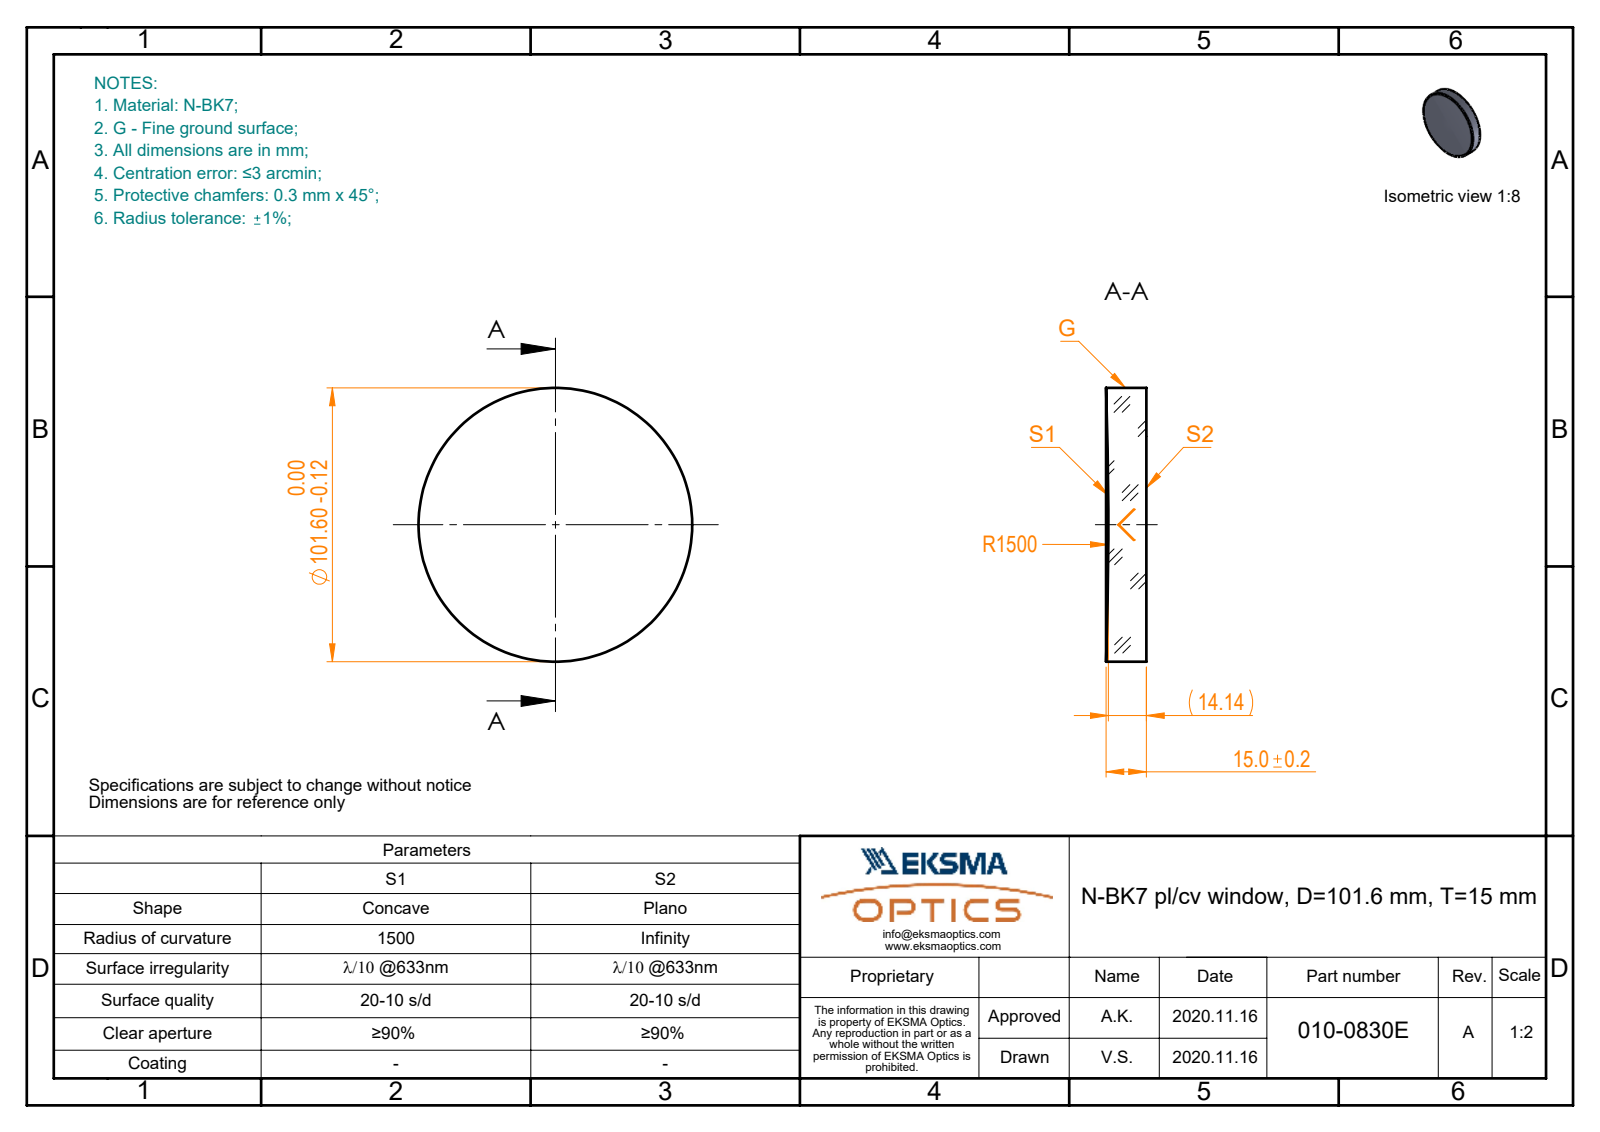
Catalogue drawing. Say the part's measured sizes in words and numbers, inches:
The part is named "010-0830E_N-BK7_PCV_window". Its 3-D file was written by "SolidWorks 2019 (CONFIG_CONTROL_DESIGN)". It is 1 solid with 5 faces: 1 planar, 2 cylindrical and 2 other. Overall it measures 4 by 4 by 0.591 inches. Its volume is 7.208 cubic inches and its surface area 32.56 square inches. Round bosses or shafts: 1 of diameter 4.
